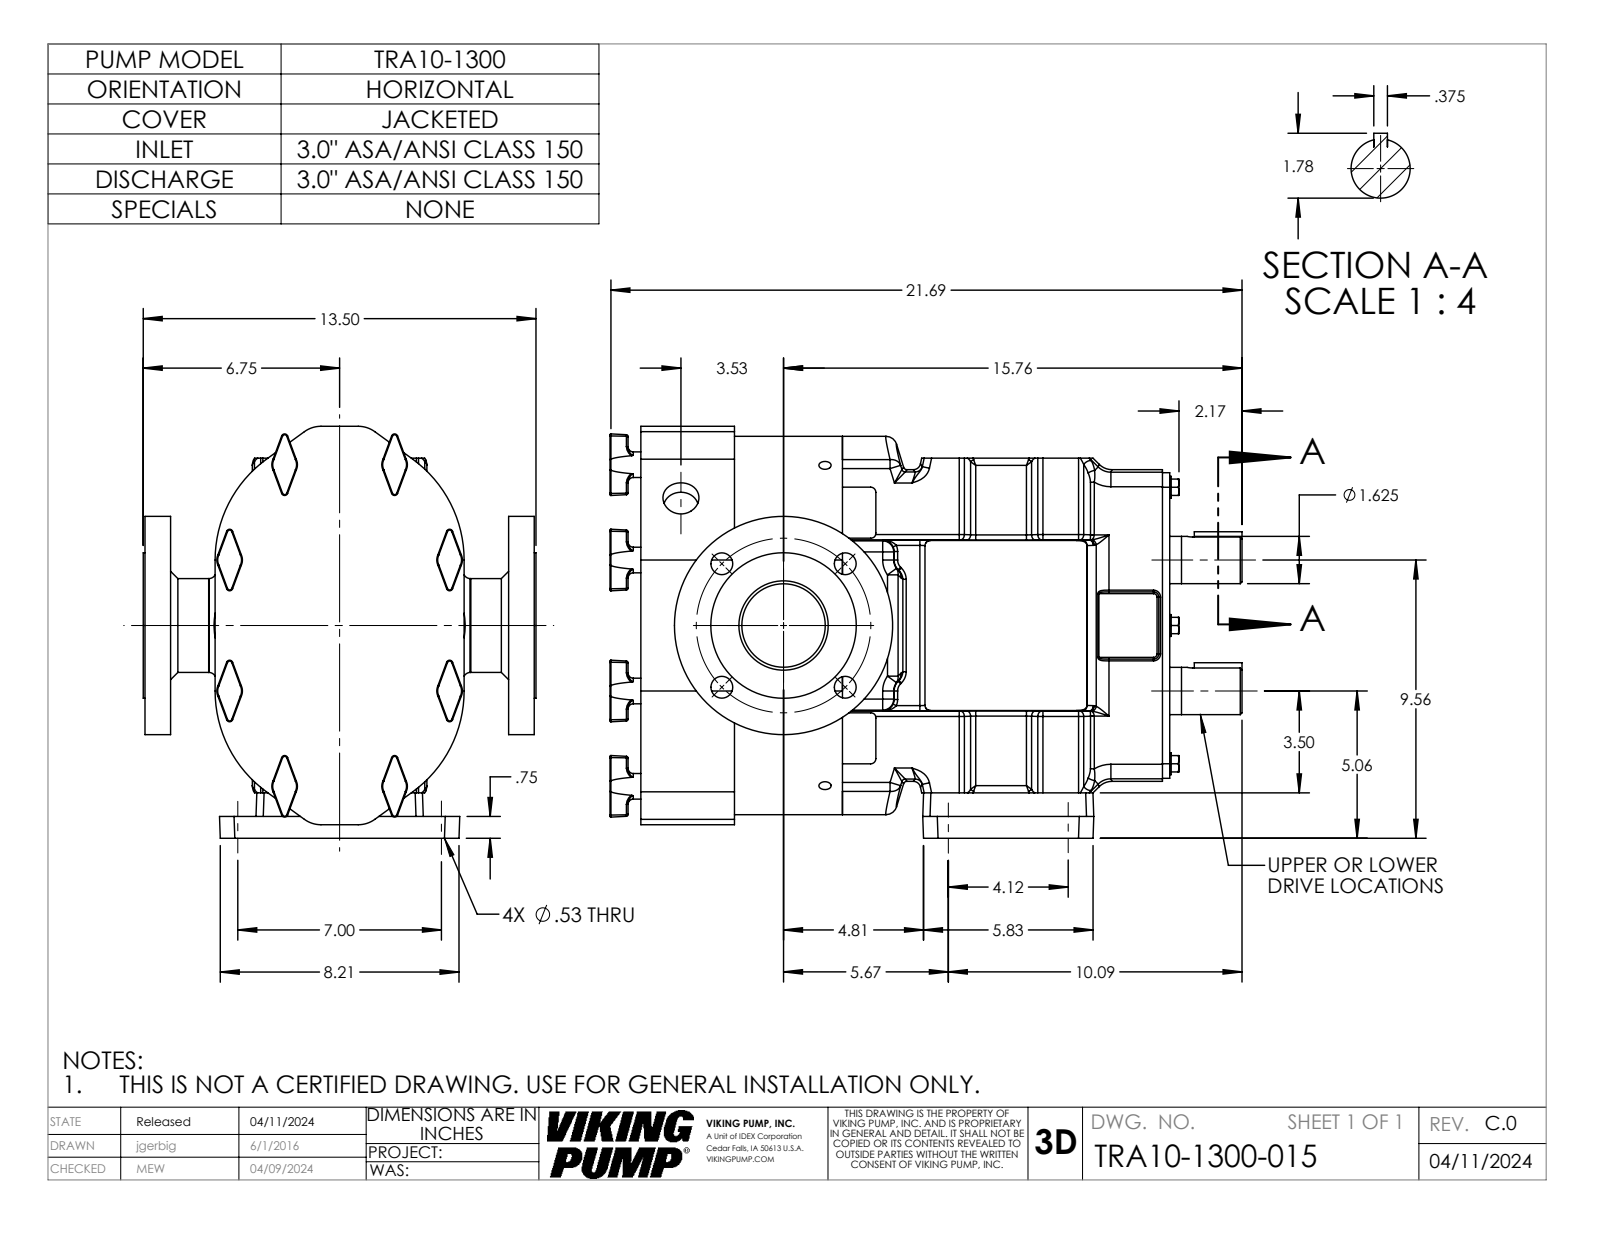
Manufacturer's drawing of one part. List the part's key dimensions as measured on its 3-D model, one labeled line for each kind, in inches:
Part name (STEP PRODUCT): 1300FLG150-30; TRA10-0600-GEARBOX-H; TRA10-1300-015; TRA10-0600-COVER-JACKET (+1 more)
STEP written by: SolidWorks 2022 (AUTOMOTIVE_DESIGN)
Units: inches
Bodies: 5 solids, 1082 faces (288 planar, 398 cylindrical, 396 other)
Overall size (bounding box): 21.724 × 14.155 × 13.5
Volume: 1 542 in³ · Surface area: 1 675 in²
Round holes (diameter × count): ⌀0.332 ×4, ⌀0.531 ×4, ⌀0.75 ×4, ⌀2.868 ×1, ⌀3.07 ×1
Round bosses / shafts (diameter × count): ⌀0.88 ×8, ⌀0.75 ×6, ⌀1.624 ×2, ⌀7.5 ×1, ⌀5 ×1, ⌀3.224 ×1
Partial cylindrical surfaces — rounded edges, fillets, slot ends (radius × count): R0.18 ×44, R0.06 ×43, R0.03 ×32, R0.25 ×30, R0.38 ×28, R0.12 ×24, R0.5 ×20, R0.375 ×12
Main face-to-face distances: 3.712, 3.218, 6.93, 0.5, 2.31, 9.31, 11.25, 18.18, 14.962, 2.81
Hole centre spacings: 3, 2.895, 4.12, 4.243, 4.243, 6, 7, 8.122
